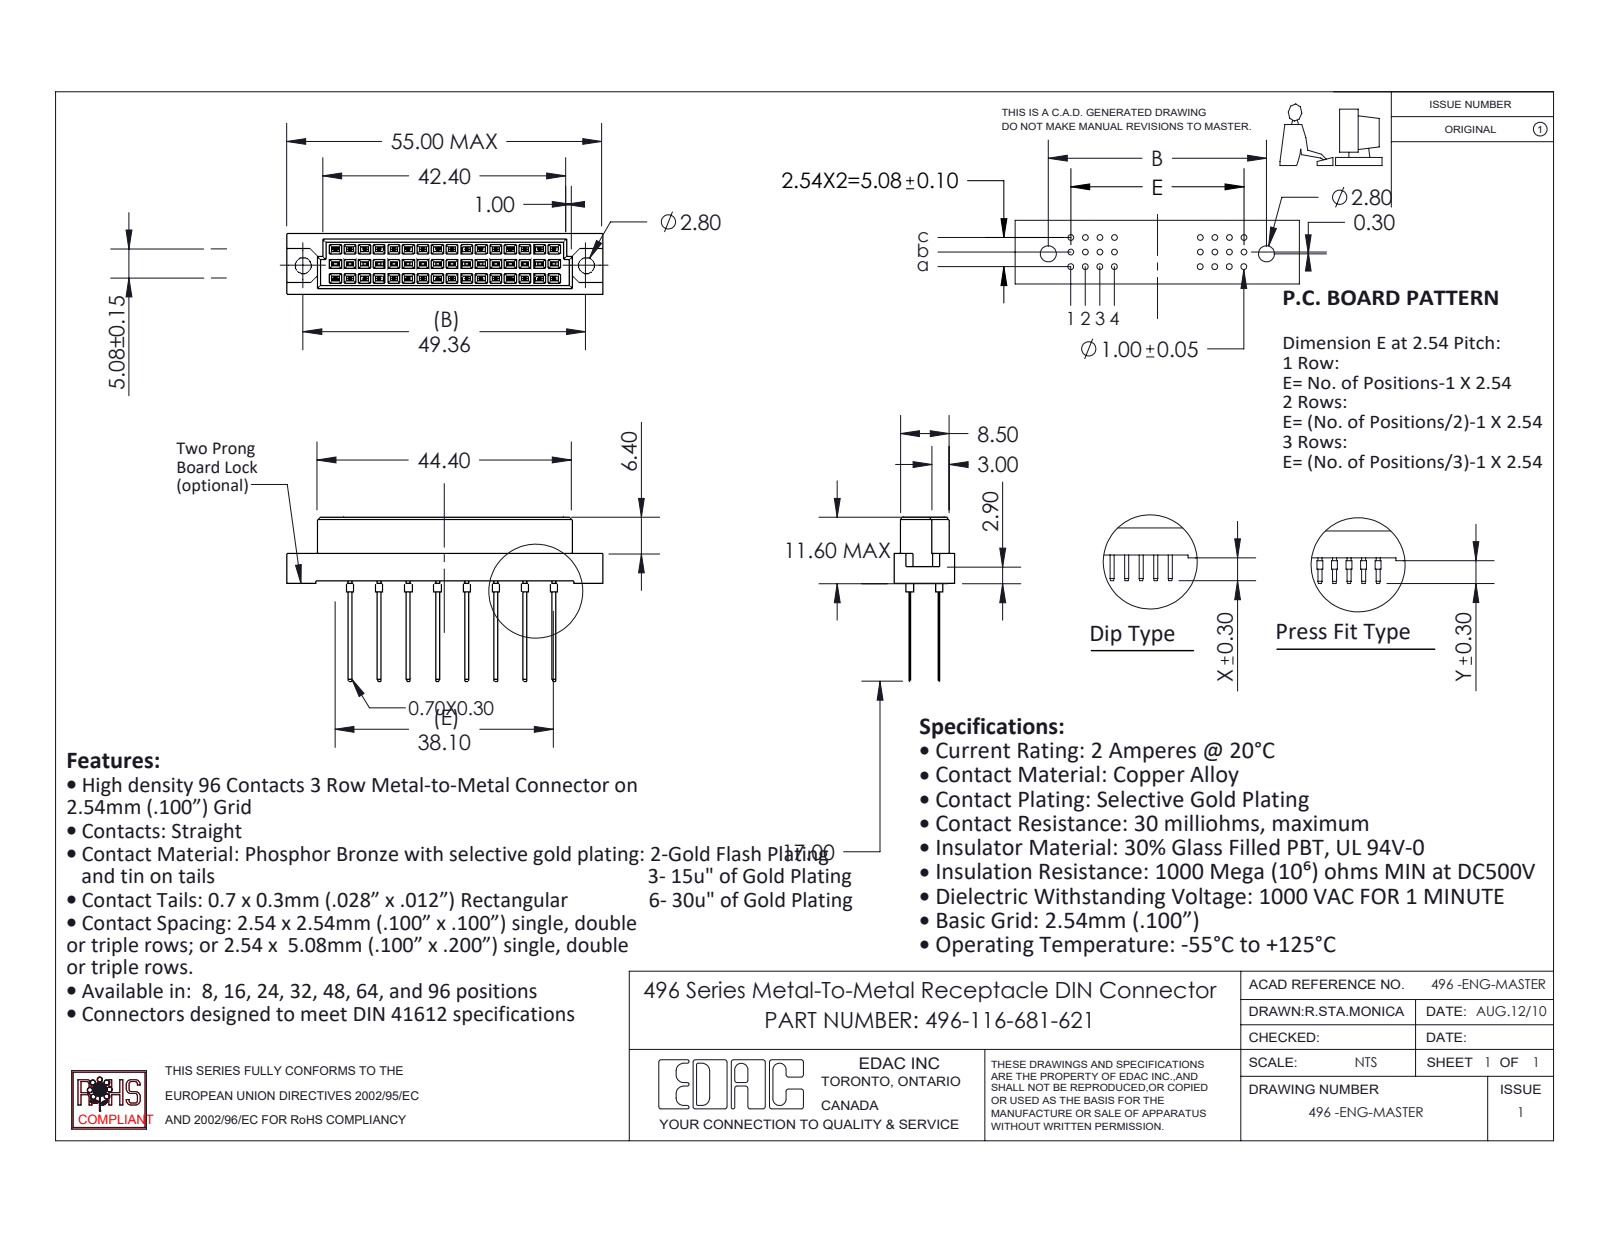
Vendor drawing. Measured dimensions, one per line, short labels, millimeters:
name: 496 Part_48; 496-116-681-621; 496-290_81
written by: SolidWorks 2020 (CONFIG_CONTROL_DESIGN)
unit: mm
bodies: 17 solids, 954 faces (918 planar, 36 cylindrical, 0 other)
size: 55 × 28.6 × 10.6
volume: 4 675 mm³; area: 4 949 mm²
holes: 2× ⌀2.8
bosses: 16× ⌀1
face distances: 5.08, 2.54, 1.05, 9.55, 0.81, 0.56, 2.61, 2.91, 7.69, 7.99
hole spacings: 49.36
